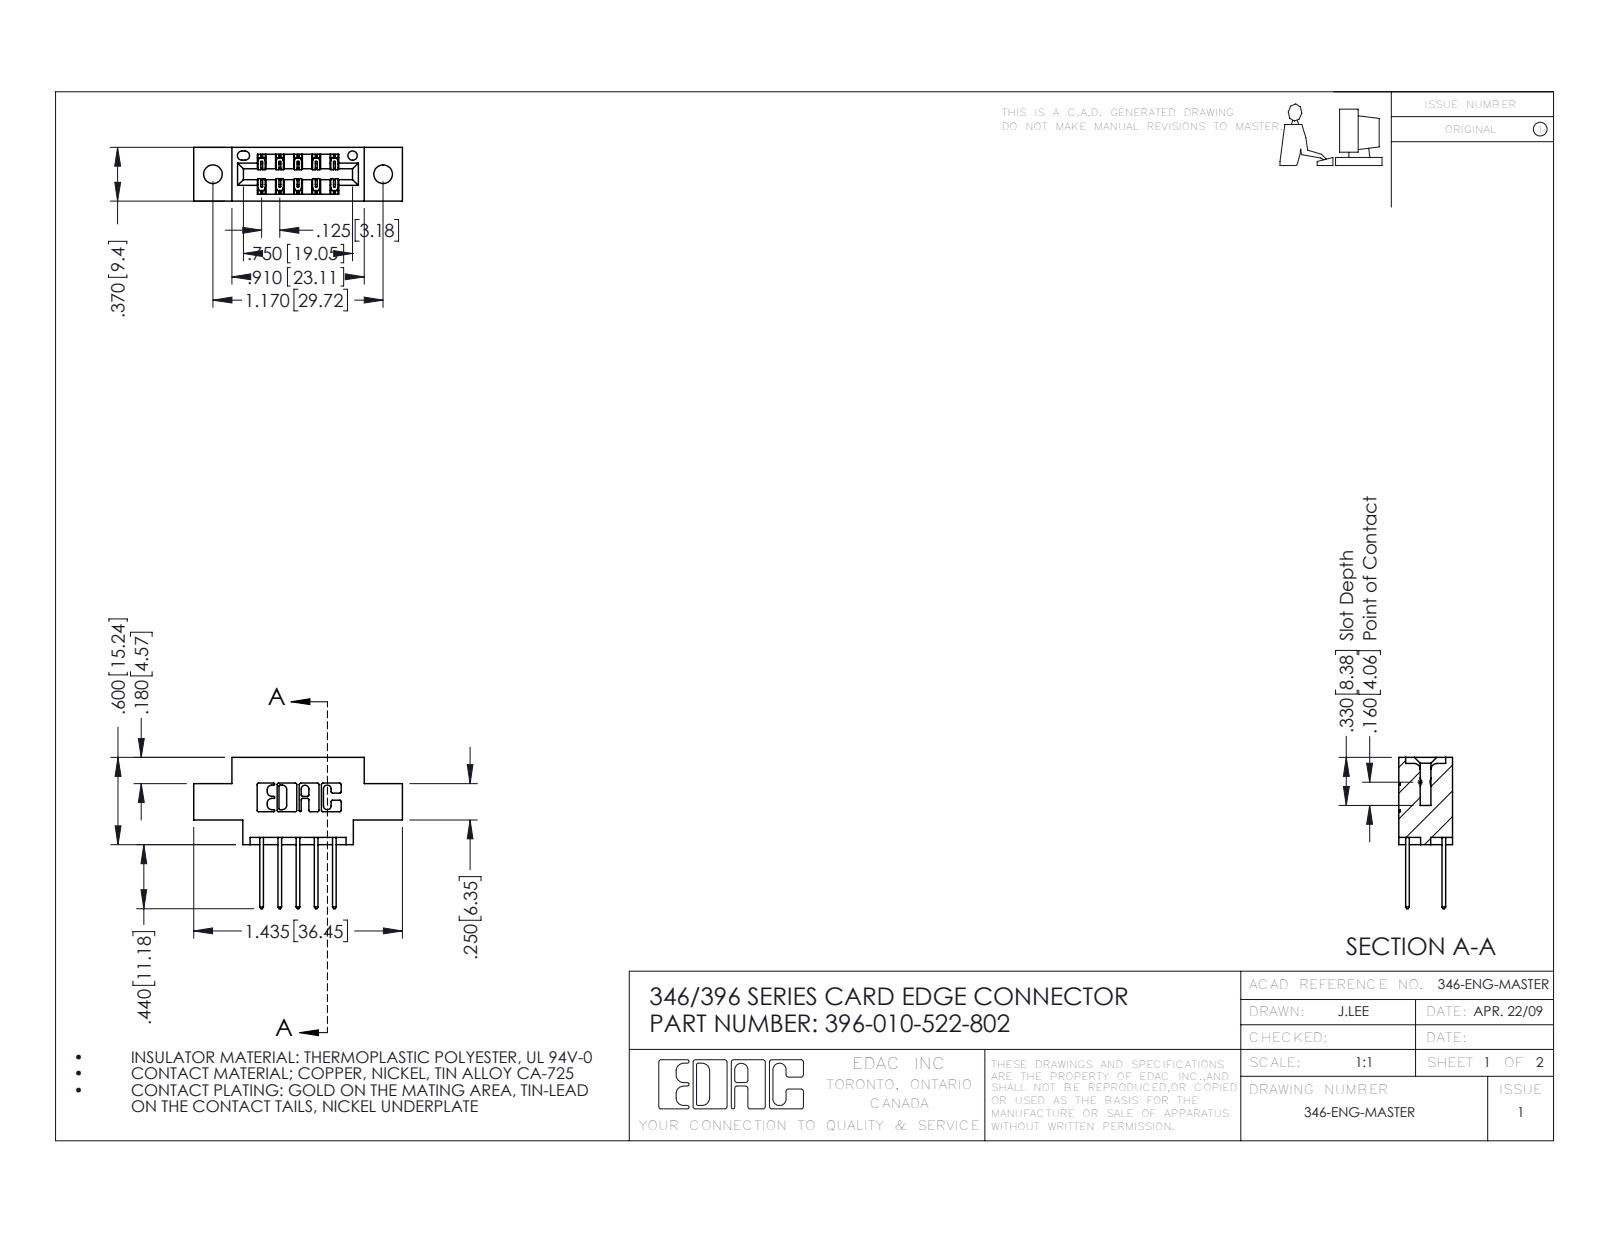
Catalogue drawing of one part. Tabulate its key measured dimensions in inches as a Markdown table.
| quantity | value |
| --- | --- |
| part name | 346 Part_0.170 Offset - 0.128 Dia; 345-292-001_345-293-122; 396-010-522-802 |
| STEP written by | SolidWorks 2016 (CONFIG_CONTROL_DESIGN) |
| units | inches |
| bodies | 11 solids, 646 faces (430 planar, 216 cylindrical, 0 other) |
| overall size | 1.435 × 1.04 × 0.37 |
| volume | 0.189 in³ |
| surface area | 5.751 in² |
| round holes (diameter × count) | 0.128 × 2, 0.064 × 1 |
| partial cylindrical surfaces (radius × count) | 0.01 × 22, 0.006 × 15, 0.01 × 10, 0.007 × 6, 0.031 × 6, 0.026 × 3, 0.014 × 2, 0.022 × 2 |
| main face-to-face distances | 0.25, 0.37, 0.048, 0.322, 0.025, 0.072, 0.298, 0.275, 0.225, 0.148 |
| hole center spacings | 0.246, 0.969, 1.17 |
